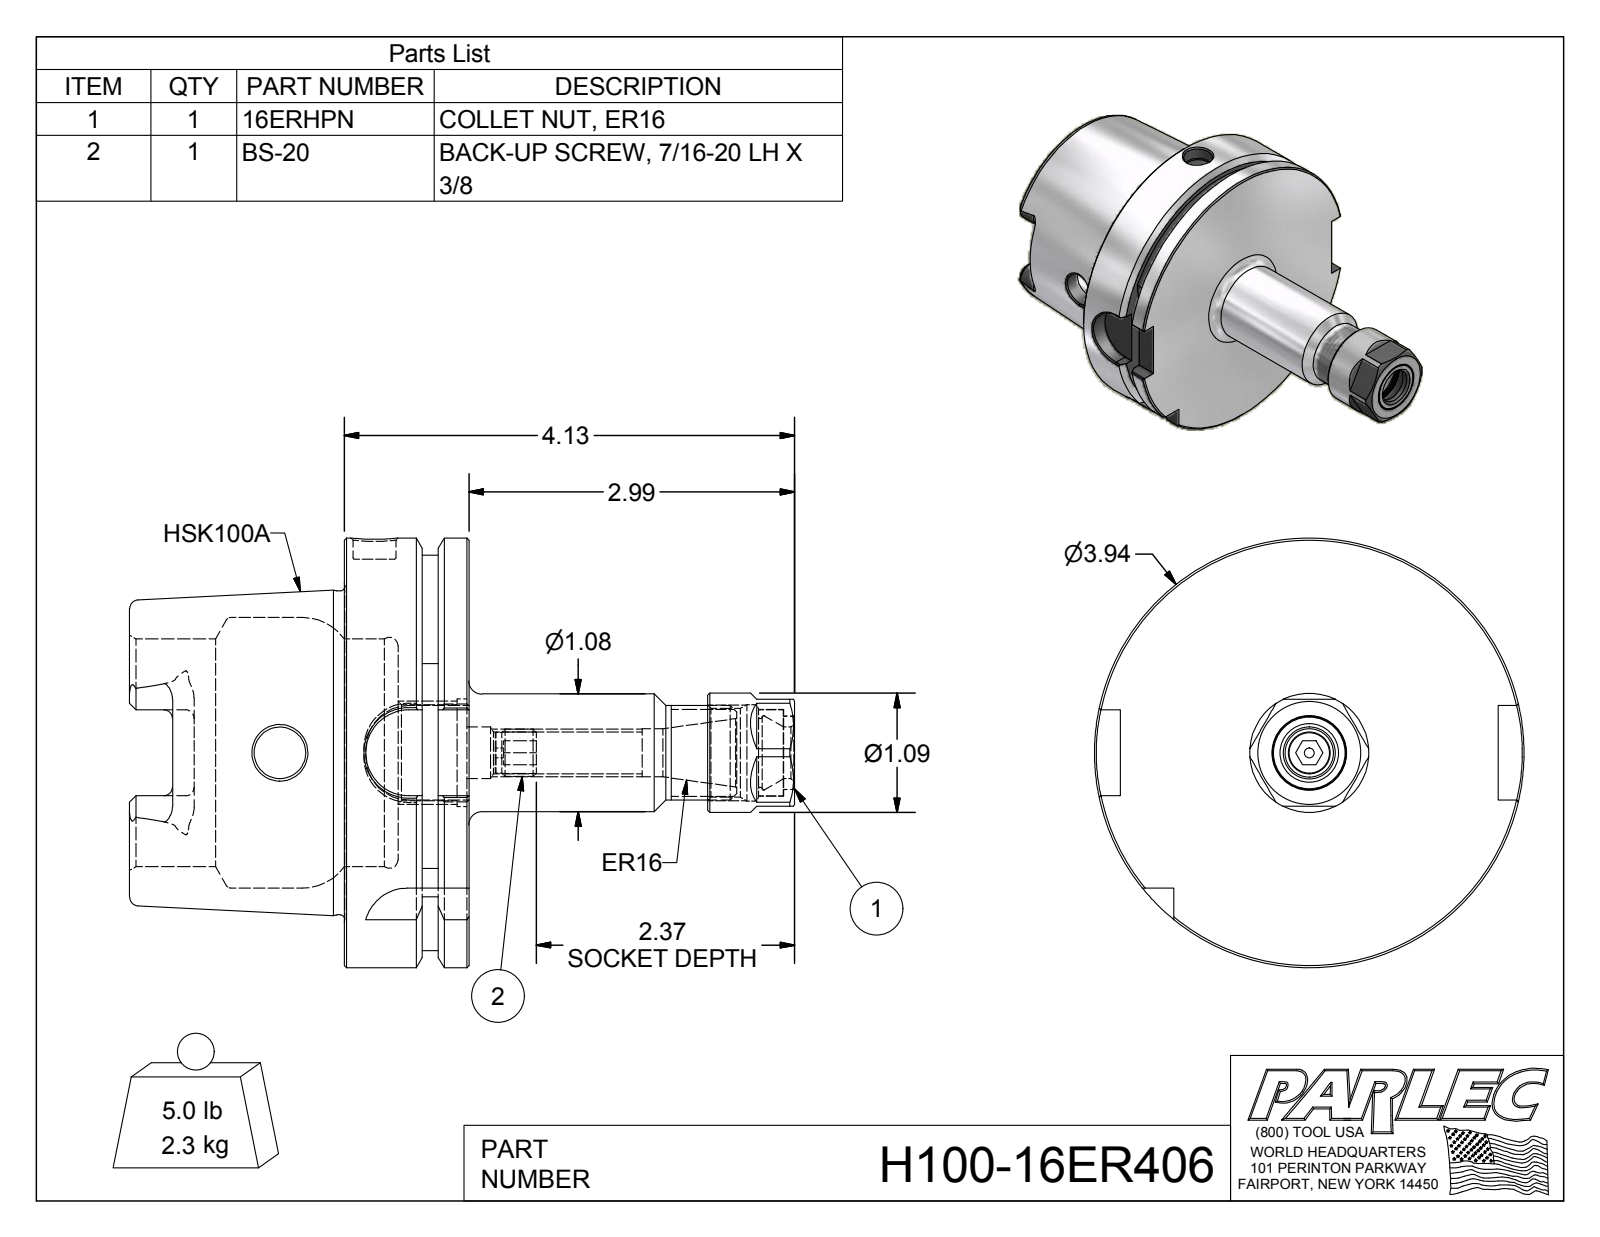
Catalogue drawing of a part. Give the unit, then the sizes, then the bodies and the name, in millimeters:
Units: millimetres
Overall size (bounding box): 154.8 × 100 × 100
Round holes (diameter × count): ⌀12 ×2, ⌀2.3 ×1, ⌀9.7 ×1, ⌀10 ×1, ⌀11.2 ×1, ⌀12 ×1, ⌀12 ×1, ⌀16 ×1, ⌀17.1 ×1, ⌀17.3 ×1, ⌀20.2 ×1, ⌀20.7 ×1
Round bosses / shafts (diameter × count): ⌀100 ×1, ⌀75.4 ×1, ⌀27.7 ×1, ⌀27.4 ×1, ⌀22 ×1, ⌀20.1 ×1, ⌀17 ×1, ⌀11 ×1
Partial cylindrical surfaces — rounded edges, fillets, slot ends (radius × count): R2 ×6, R4.9 ×4, R10 ×4, R46 ×1
Main face-to-face distances: 29, 12.5, 16.5, 50, 62.5, 79, 71.9, 21.9, 9.4, 7.1
Volume: 287 300 mm³ · Surface area: 62 300 mm²
Bodies: 4 solids, 188 faces (73 planar, 49 cylindrical, 66 other)
Part name (STEP PRODUCT): H100-16ER406; H100-16ER4-1; BS-20; 16ERHPN
STEP written by: Autodesk Inventor 2012 (AUTOMOTIVE_DESIGN)
